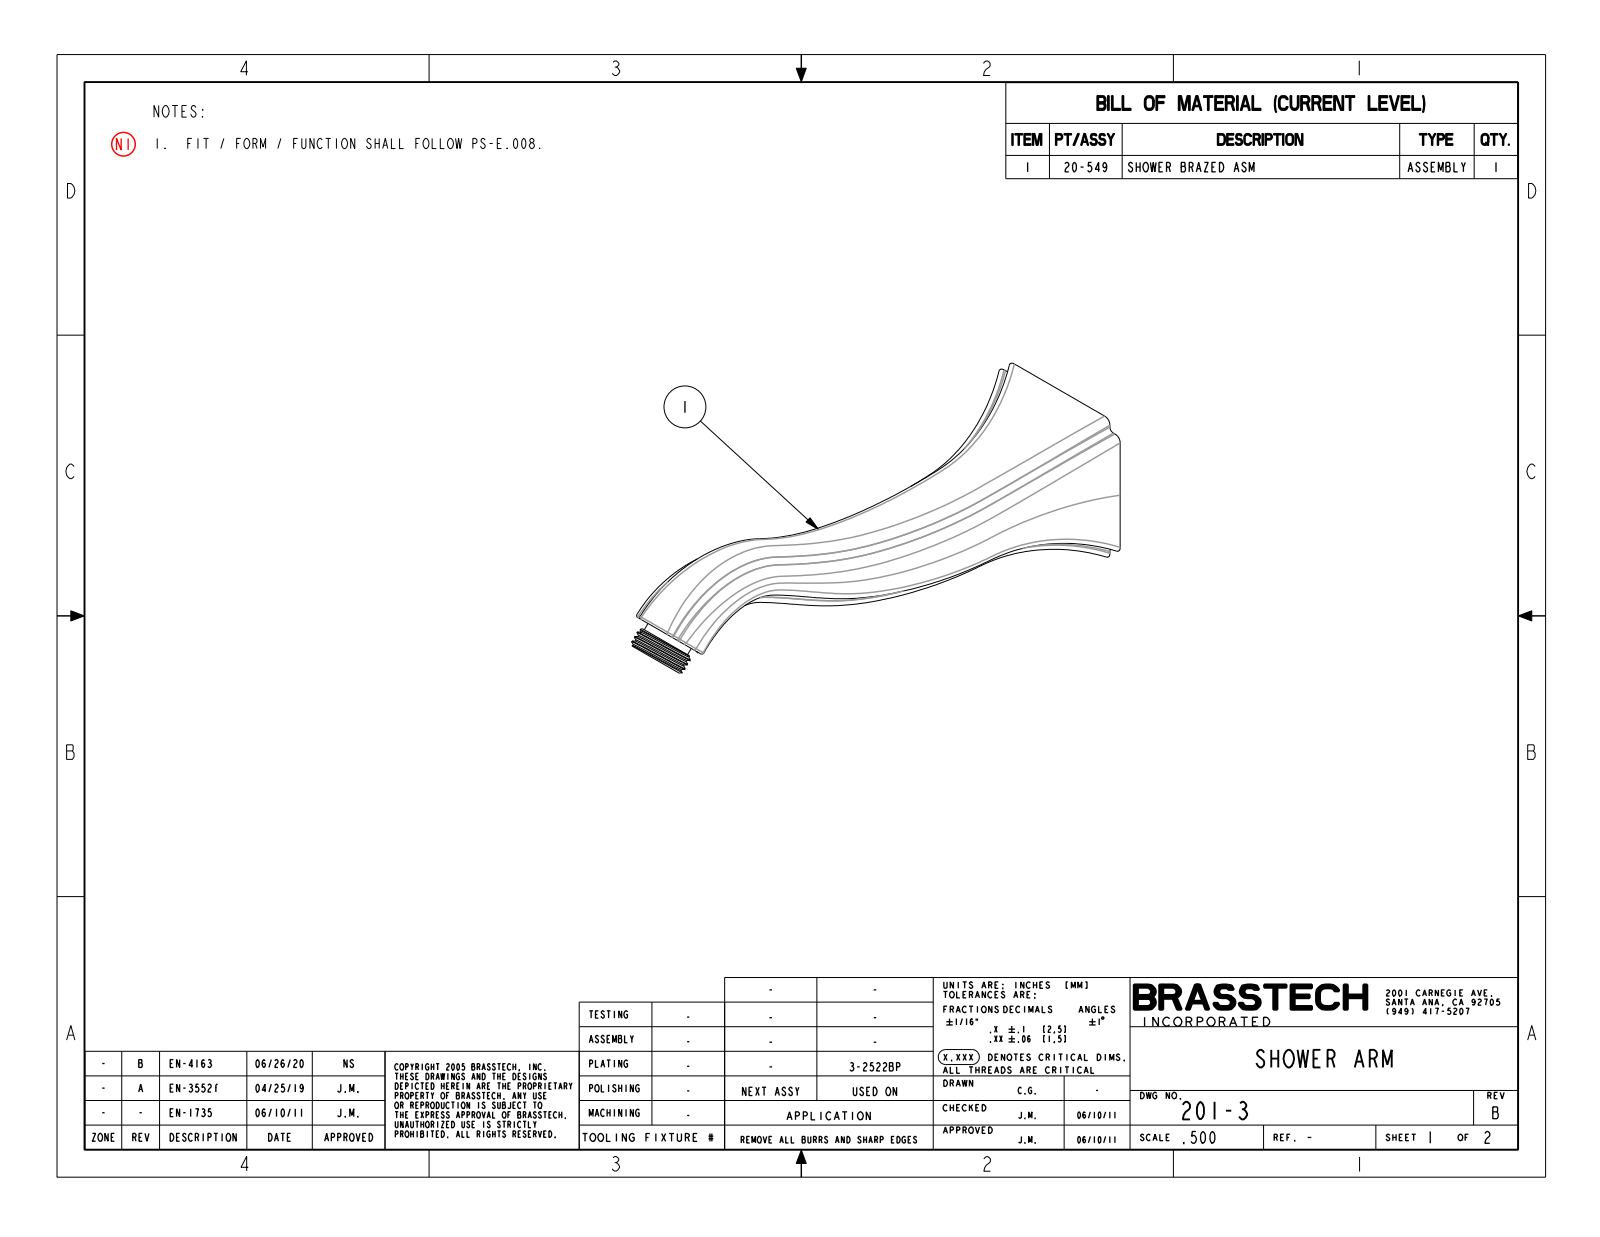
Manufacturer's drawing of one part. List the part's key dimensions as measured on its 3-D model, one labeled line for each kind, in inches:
Part name (STEP PRODUCT): 201-3
STEP written by: CREO PARAMETRIC BY PTC INC, 2018400 (AUTOMOTIVE_DESIGN)
Units: inches
Bodies: 1 solid, 79 faces (6 planar, 11 cylindrical, 62 other)
Overall size (bounding box): 8.122 × 2.857 × 2.36
Volume: 10.57 in³ · Surface area: 41.58 in²
Round holes (diameter × count): ⌀0.469 ×1
Round bosses / shafts (diameter × count): ⌀2 ×1, ⌀0.823 ×1, ⌀0.687 ×1
Main face-to-face distances: 0.378, 0.158, 0.22, 0.278, 0.12, 0.1
